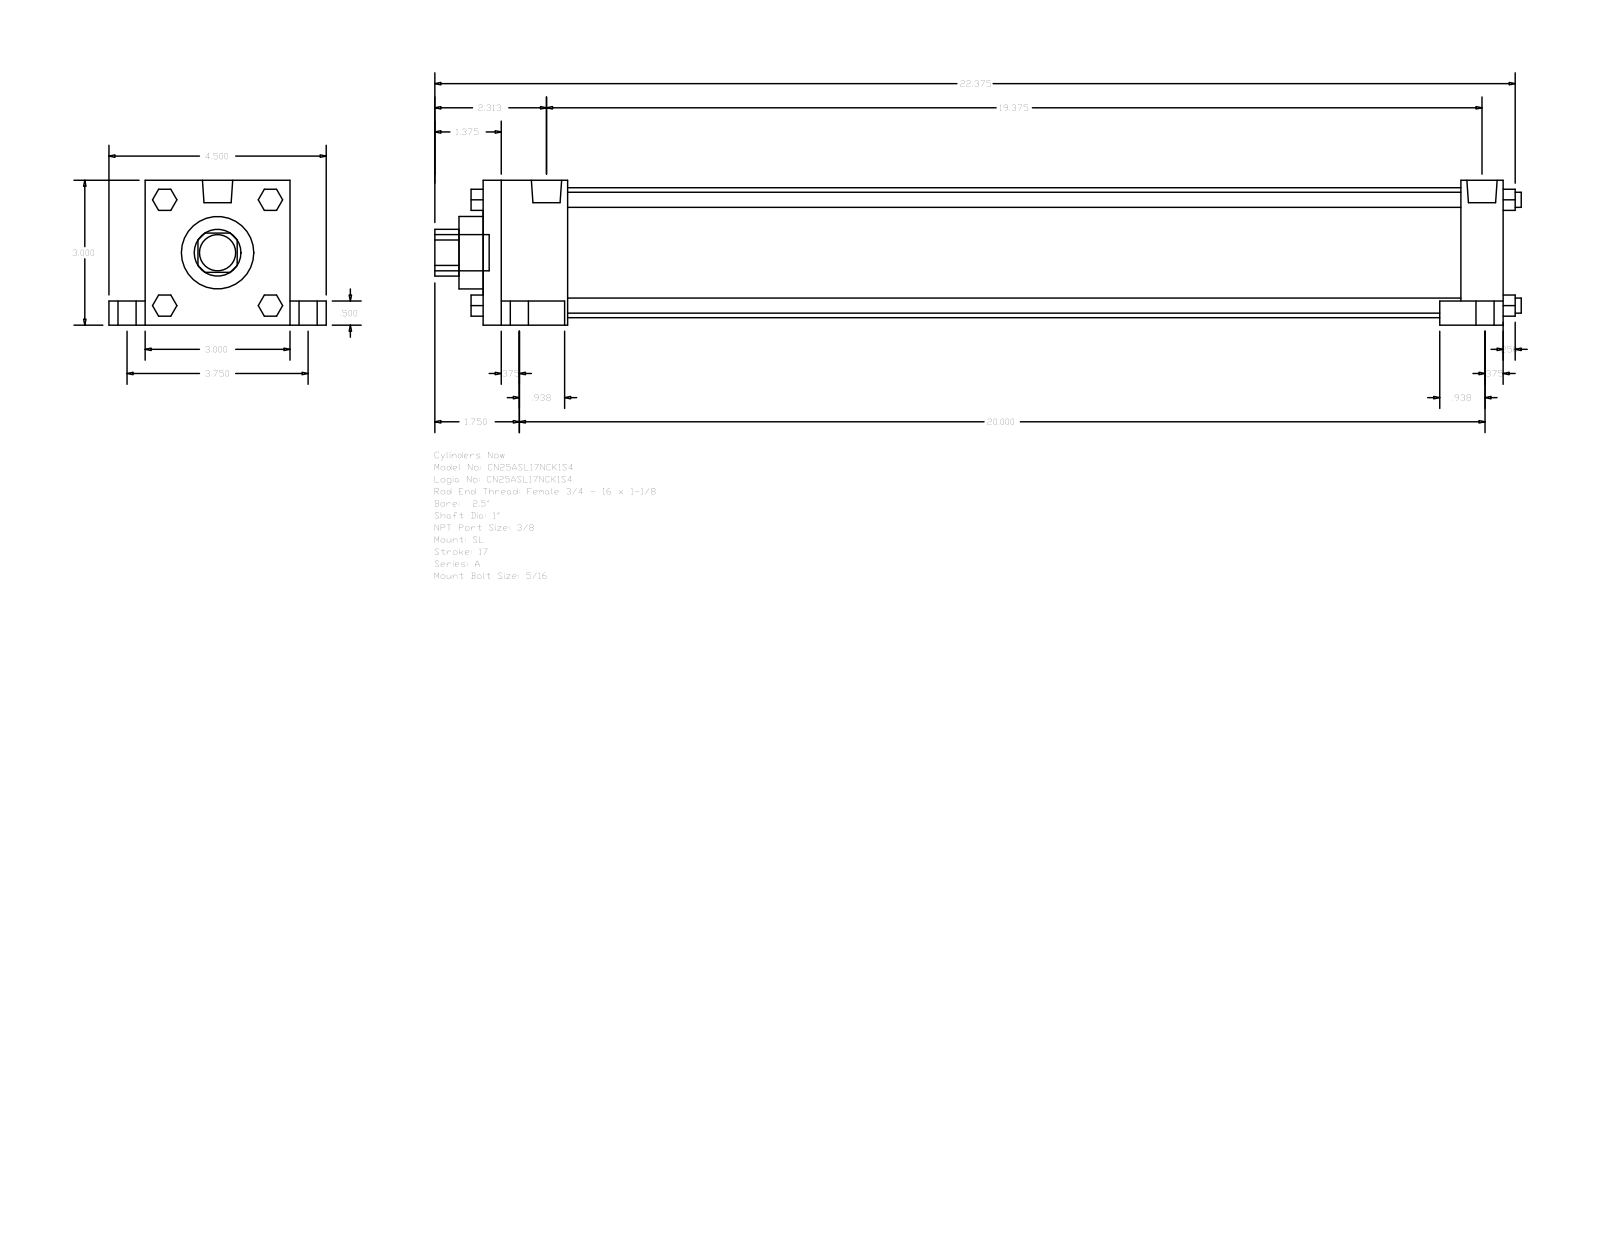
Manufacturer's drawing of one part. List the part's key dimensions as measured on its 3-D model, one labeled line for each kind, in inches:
Part name (STEP PRODUCT): A_SL__0250_1
STEP written by: GSSL Pune (CONFIG_CONTROL_DESIGN)
Units: inches
Bodies: 0 solids, 148 faces (112 planar, 36 cylindrical, 0 other)
Overall size (bounding box): 22.5 × 4.5 × 3
Round holes (diameter × count): ⌀1 ×1, ⌀1.5 ×1, ⌀2.69 ×1
Round bosses / shafts (diameter × count): ⌀0.625 ×4, ⌀0.375 ×4, ⌀0.313 ×4, ⌀0.219 ×4, ⌀0.627 ×2, ⌀0.75 ×1
Partial cylindrical surfaces — rounded edges, fillets, slot ends (radius × count): R0.484 ×1
Main face-to-face distances: 3, 21.125, 0.5, 1.75, 19.375, 20.25, 18.5, 0.875, 0.75, 2.5
